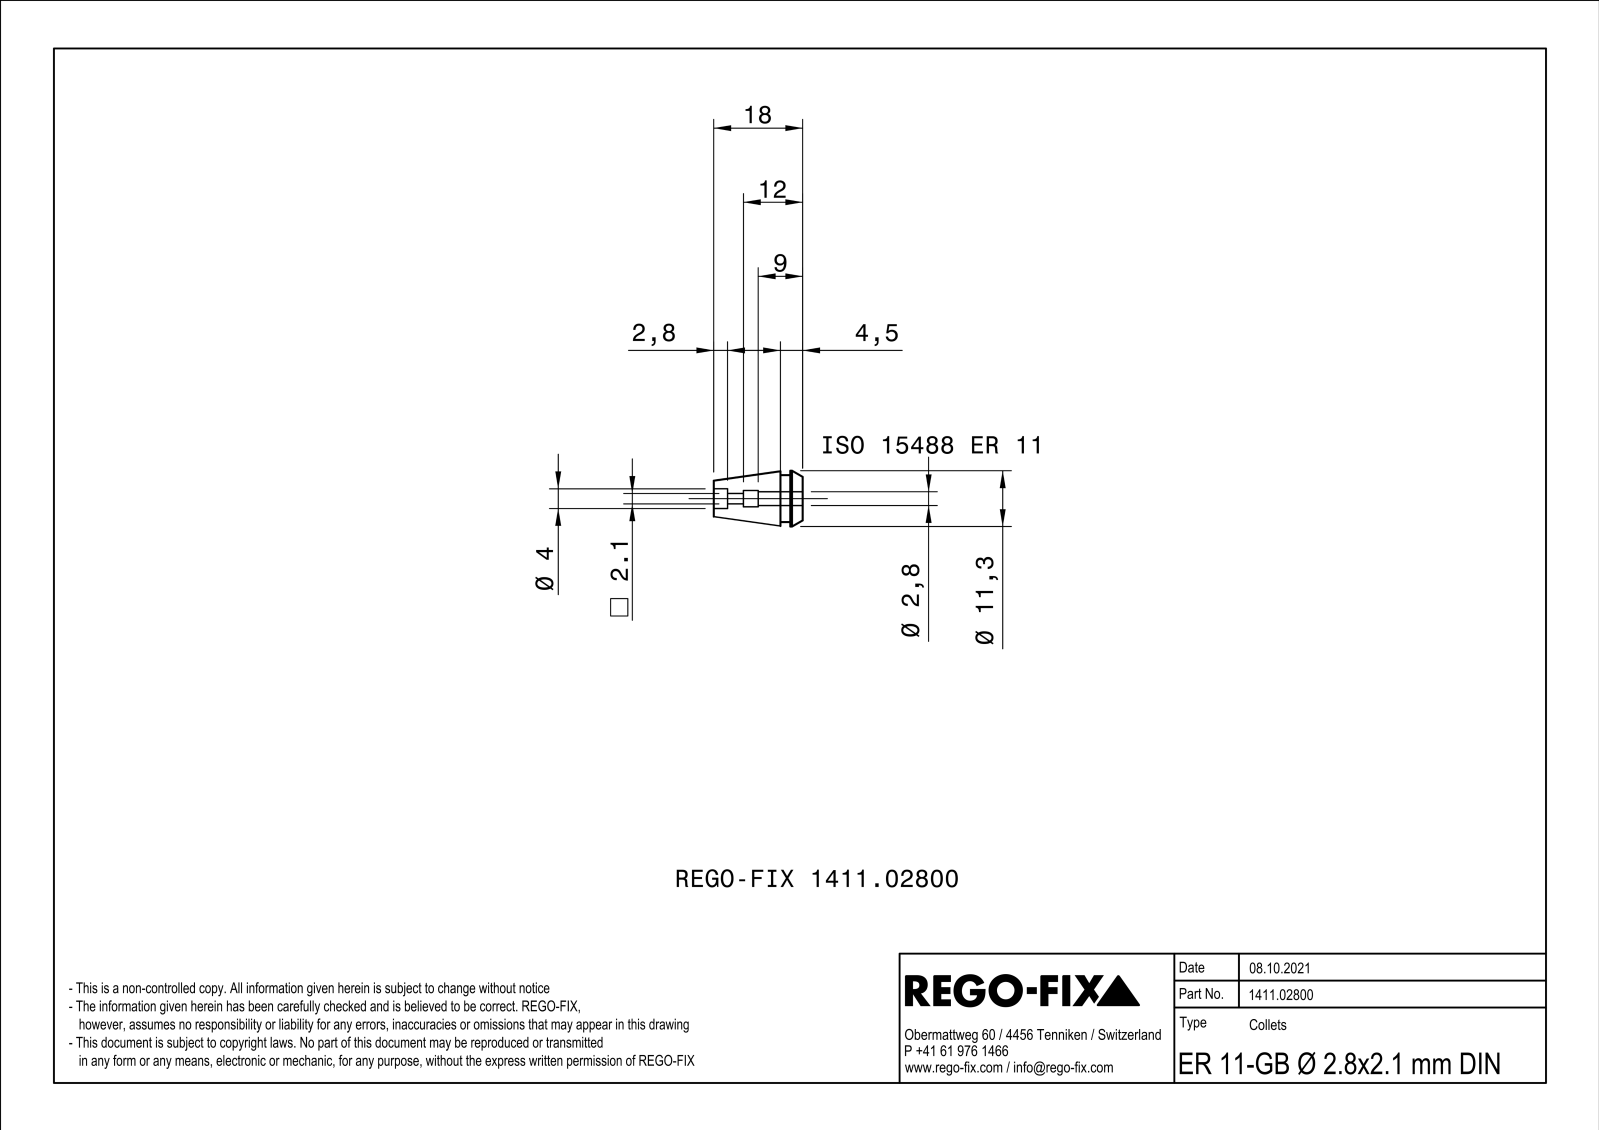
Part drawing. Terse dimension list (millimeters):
name: NOCUT
written by: SIEMENS PLM Software Solid Edge ST10 (AUTOMOTIVE_DESIGN)
unit: mm
bodies: 1 solid, 144 faces (68 planar, 32 cylindrical, 44 other)
size: 18 × 11.29 × 11.29
volume: 924 mm³; area: 1 535 mm²
holes: 1× ⌀4
bosses: 1× ⌀11.3, 1× ⌀9.5
rounds: 1× R1.25, 1× R1.4, 1× R1.65
face distances: 0.5, 13.5, 2.5, 4.5, 2, 18, 15.5, 1.5, 3, 15
